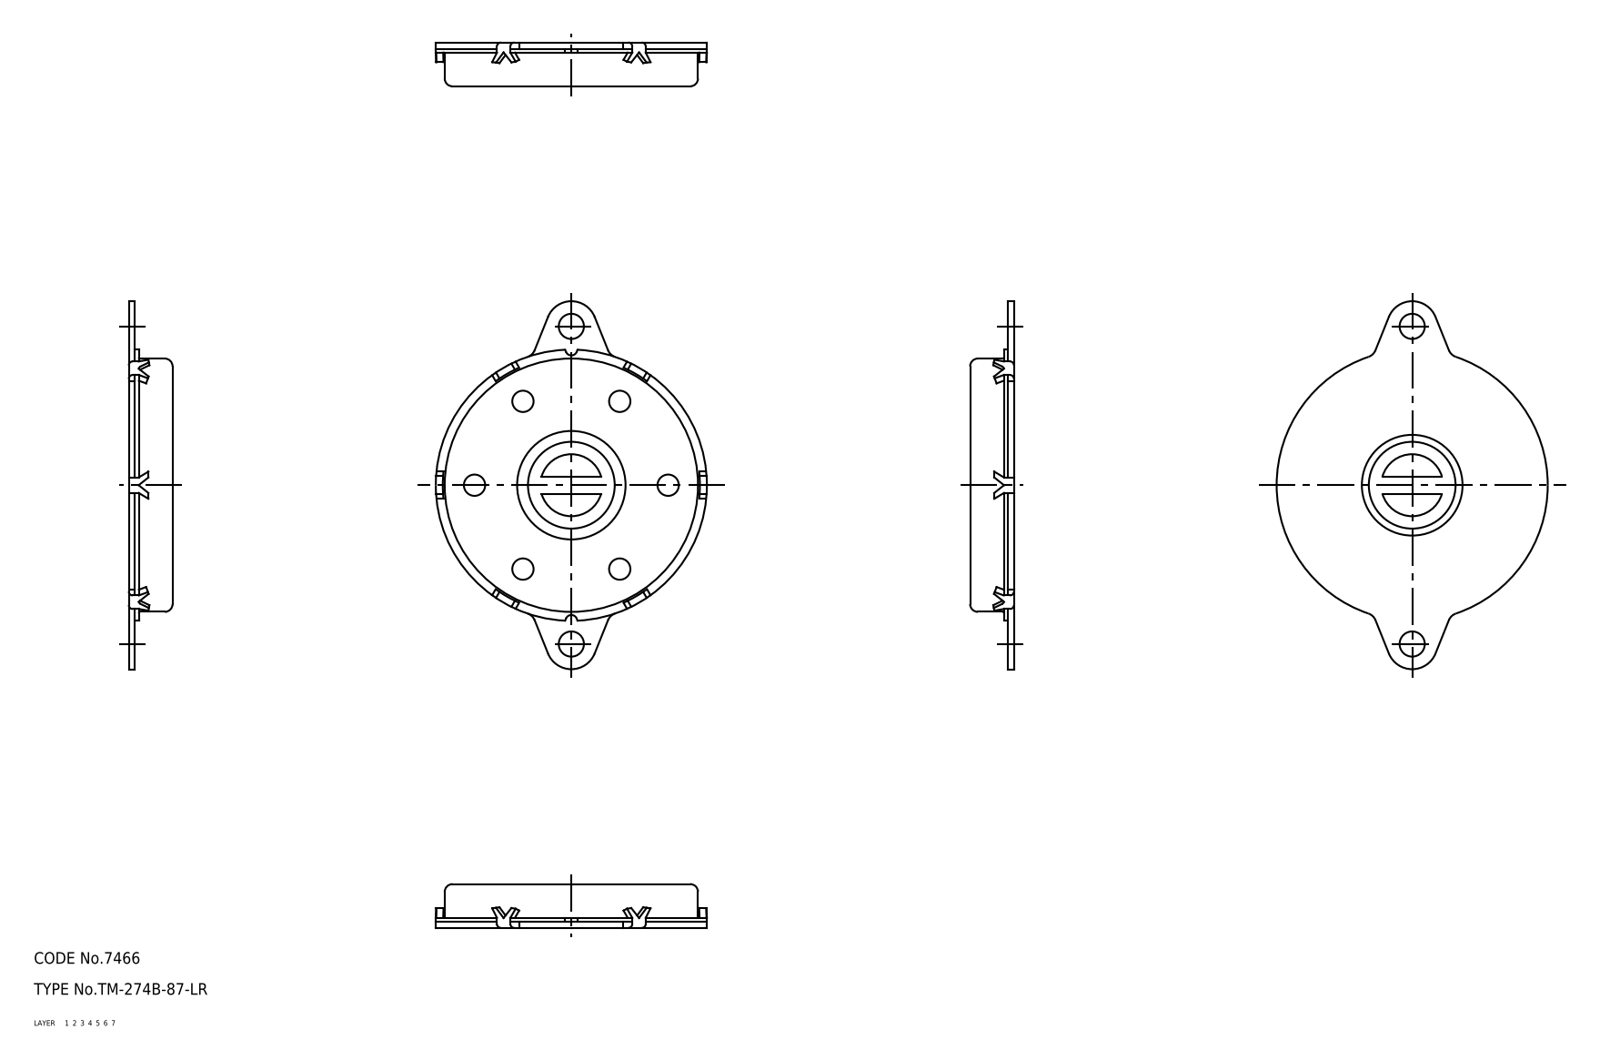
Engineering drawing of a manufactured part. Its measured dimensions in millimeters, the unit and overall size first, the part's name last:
Units: millimetres
Overall size (bounding box): 95 × 70 × 11.3
Volume: 36 857 mm³ · Surface area: 13 592 mm²
Bodies: 2 solids, 199 faces (0 planar, 0 cylindrical, 199 other)
Part name (STEP PRODUCT): inner ring; TM_274B_87_LR_818_36
STEP written by: CADfix (AUTOMOTIVE_DESIGN)
